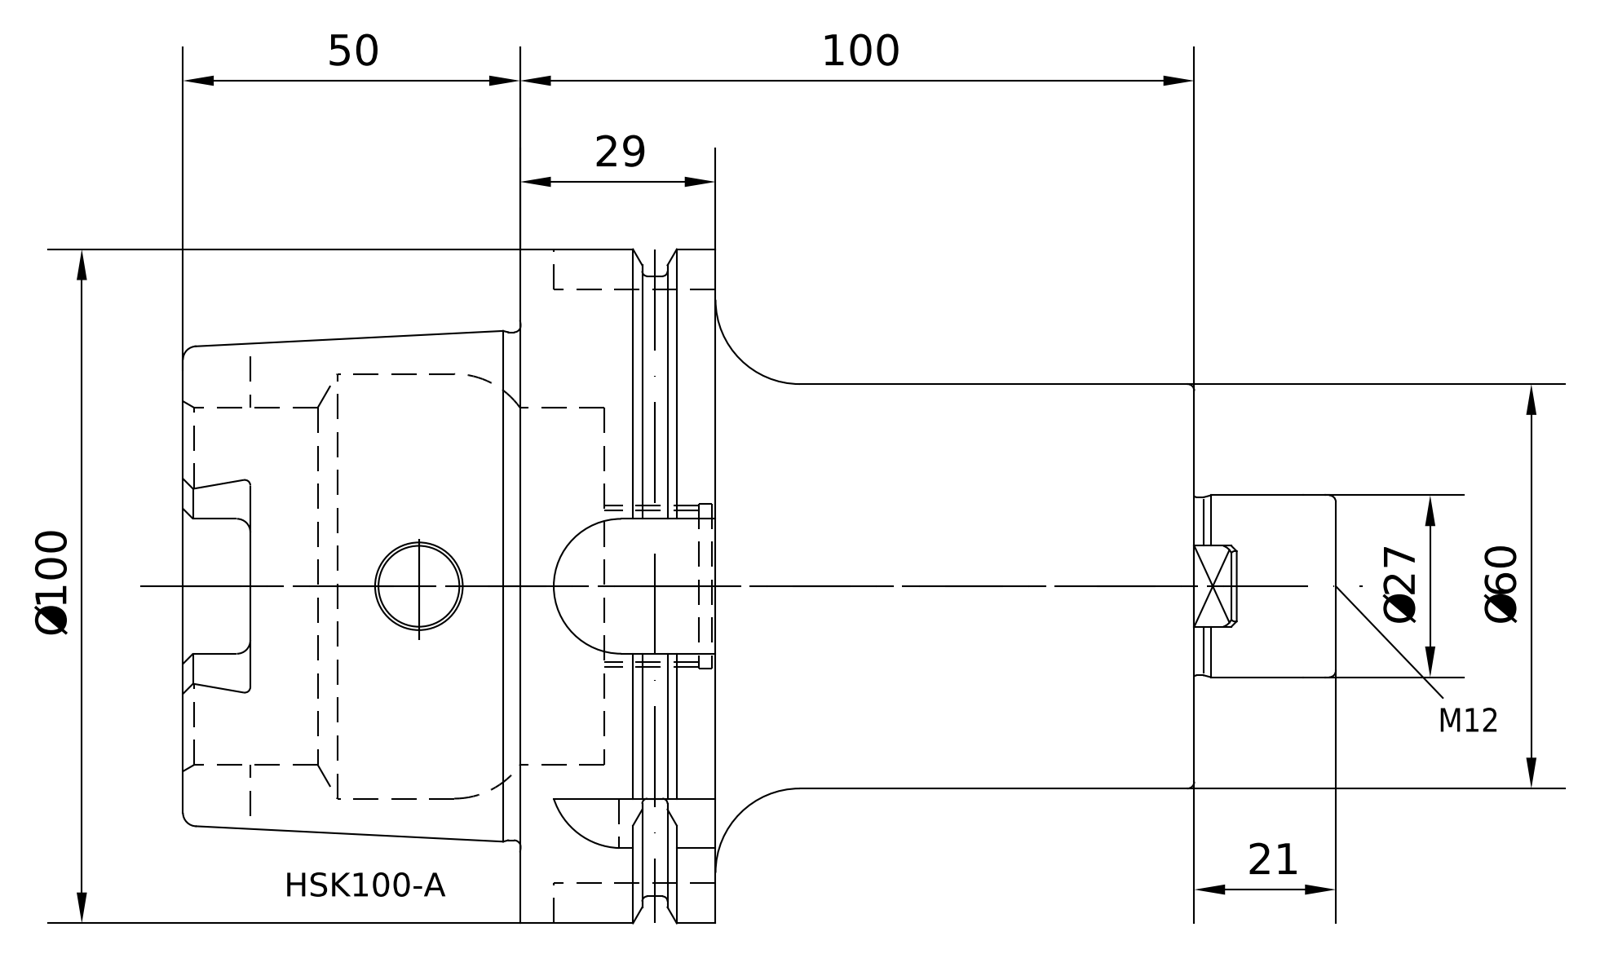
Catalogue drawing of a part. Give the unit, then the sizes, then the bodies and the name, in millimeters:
Units: millimetres
Overall size (bounding box): 171 × 100 × 100
Round holes (diameter × count): ⌀12 ×2, ⌀10 ×1, ⌀10.2 ×1, ⌀22.5 ×1, ⌀24 ×1, ⌀24.32 ×1, ⌀24.5 ×1, ⌀53 ×1, ⌀63 ×1
Round bosses / shafts (diameter × count): ⌀100 ×1, ⌀92 ×1, ⌀75.36 ×1, ⌀60 ×1, ⌀27 ×1
Partial cylindrical surfaces — rounded edges, fillets, slot ends (radius × count): R2 ×6, R5 ×4, R8 ×1, R10 ×1, R11 ×1
Main face-to-face distances: 29, 100, 71, 12.5, 16.5, 87.5, 50, 62.5, 79, 150
Volume: 472 830 mm³ · Surface area: 67 043 mm²
Bodies: 1 solid, 191 faces (61 planar, 55 cylindrical, 75 other)
Part name (STEP PRODUCT): A100-051-27
STEP written by: PRO/ENGINEER BY PARAMETRIC TECHNOLOGY CORPORATION, 2010430 (CONFIG_CONTROL_DESIGN)
